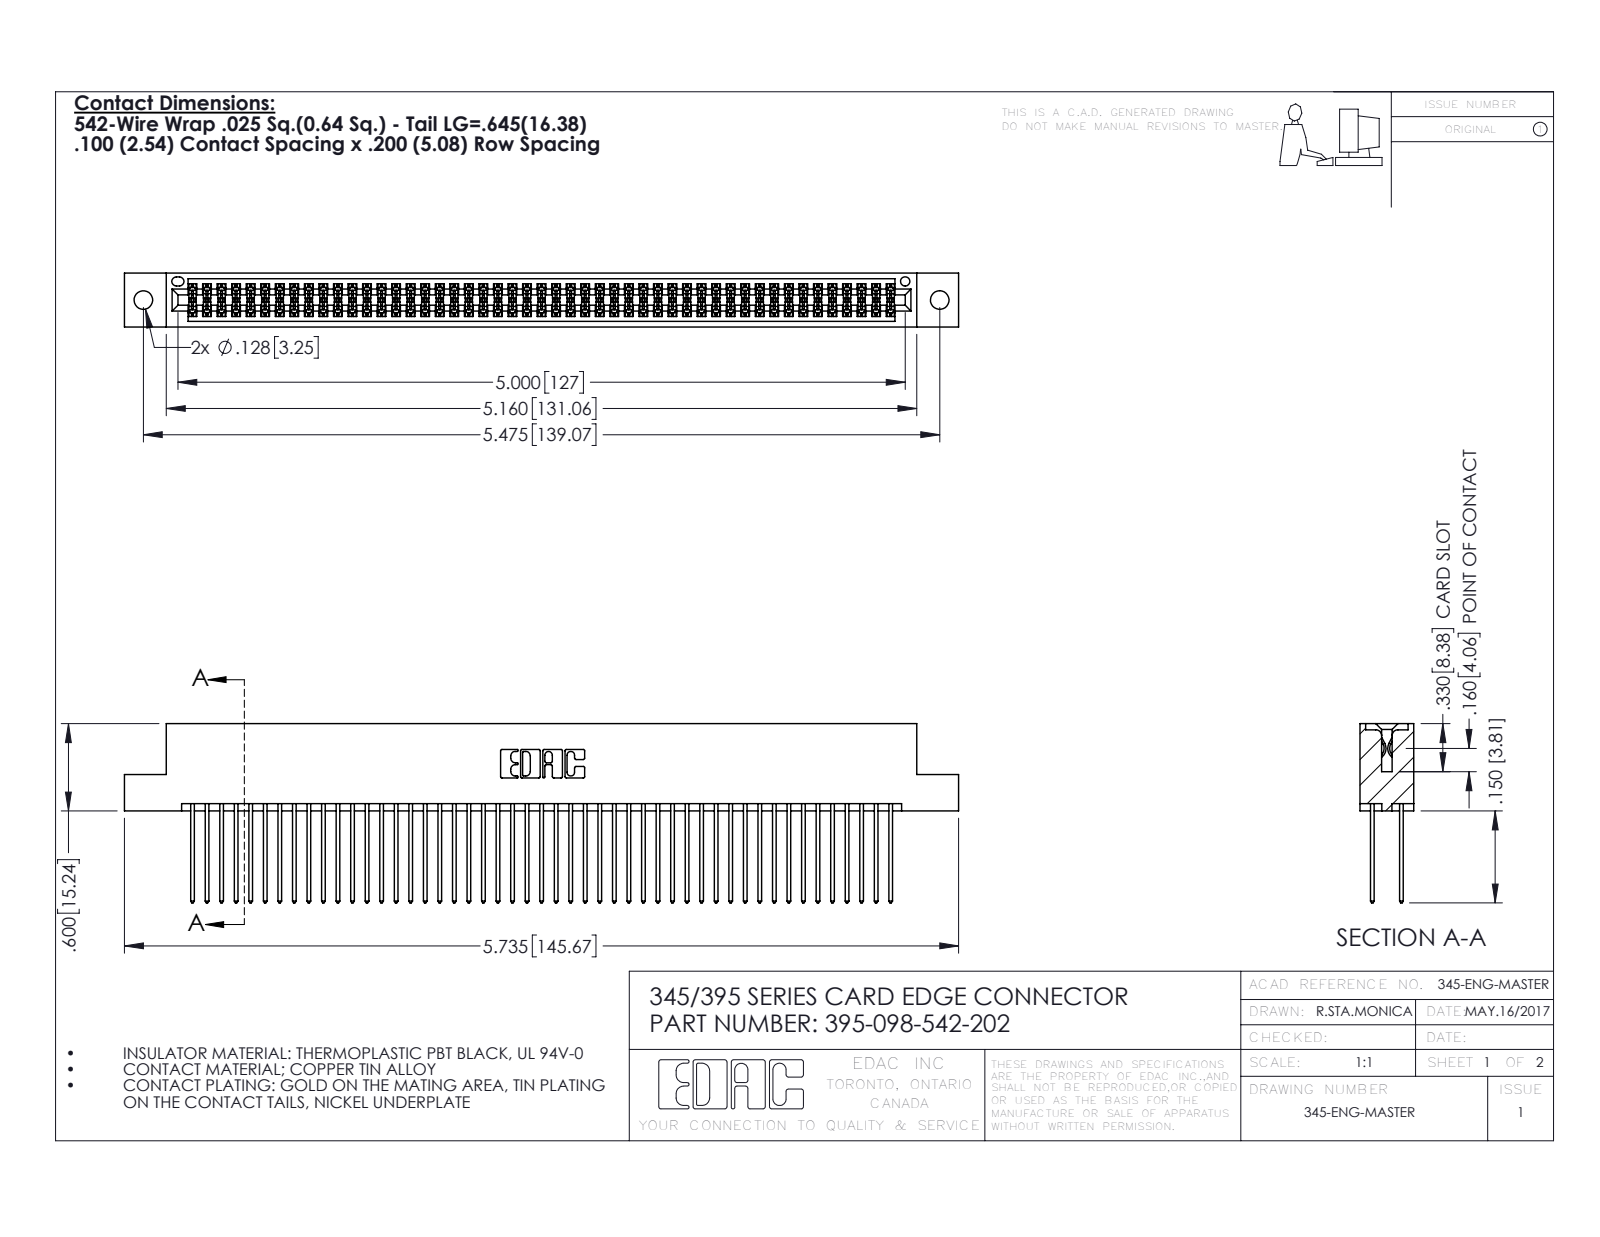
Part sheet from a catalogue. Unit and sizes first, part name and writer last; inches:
Units: inches
Overall size (bounding box): 5.735 × 1.232 × 0.37
Round holes (diameter × count): ⌀0.128 ×2, ⌀0.064 ×1
Partial cylindrical surfaces — rounded edges, fillets, slot ends (radius × count): R0.006 ×147, R0.01 ×98, R0.01 ×22, R0.007 ×6, R0.031 ×6, R0.026 ×3, R0.014 ×2, R0.019 ×2
Main face-to-face distances: 0.298, 0.072, 0.2, 0.098, 0.272, 0.025, 0.225, 0.37, 0.175, 0.149
Hole centre spacings: 0.27, 5.239, 5.475
Volume: 0.893 in³ · Surface area: 36.63 in²
Bodies: 99 solids, 5026 faces (3314 planar, 1712 cylindrical, 0 other)
Part name (STEP PRODUCT): 345 Part_Flush Mounting Lugs - 0.128 Dia; 395-098-542-202; 345-292-001_345-293-142
STEP written by: SolidWorks 2016 (CONFIG_CONTROL_DESIGN)
